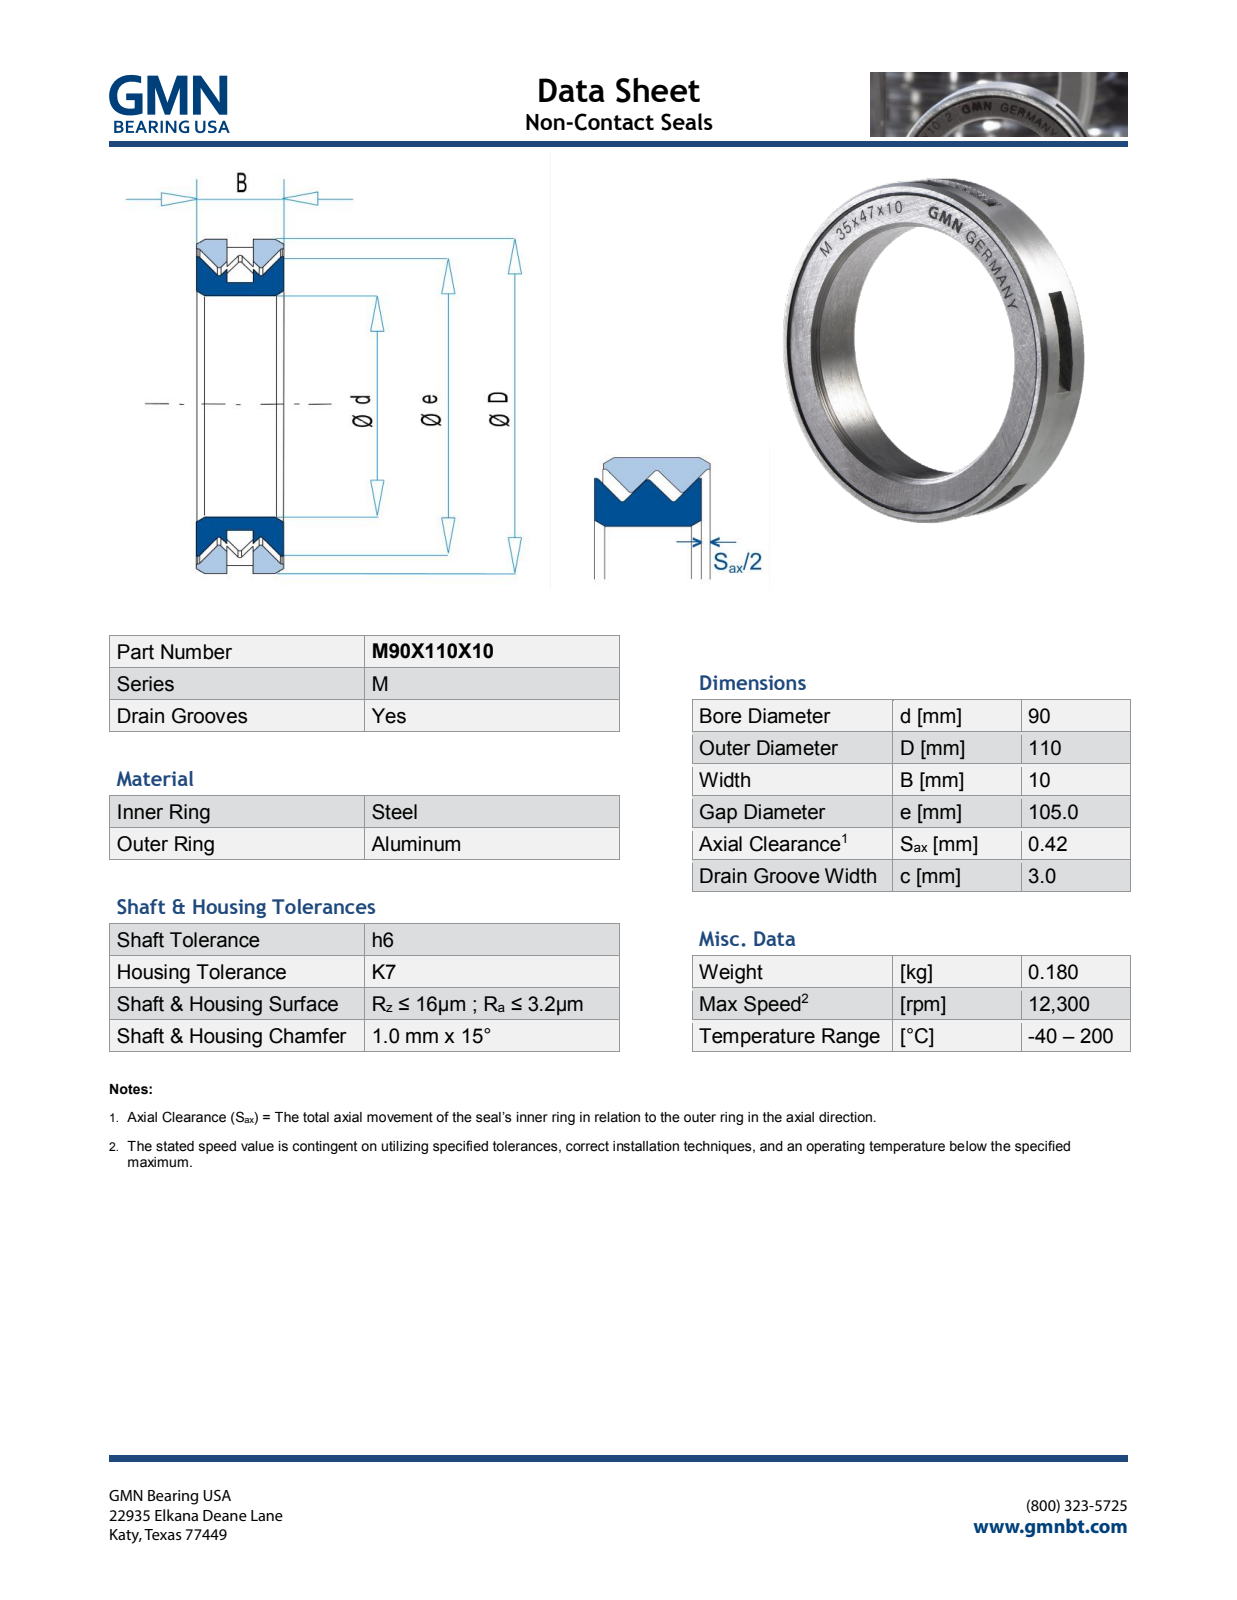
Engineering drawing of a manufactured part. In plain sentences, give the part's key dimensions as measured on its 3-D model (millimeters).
The part is named "M90X110X10_PRT". Its 3-D file was written by "PRO/ENGINEER BY PARAMETRIC TECHNOLOGY CORPORATION, 2013150 (AUTOMOTIVE_DESIGN)". It is 2 solids with 657 faces: 570 planar, 33 cylindrical and 54 other. Overall it measures 110 by 110 by 10.07 millimeters. Its volume is 29 083 cubic millimeters and its surface area 20 910 square millimeters. Round holes: 1 of diameter 90, 1 of diameter 105.3. Round bosses or shafts: 1 of diameter 110, 1 of diameter 105. Partial cylindrical surfaces (rounded edges, fillets, slot ends): 7 of radius 10. The main face-to-face distances are 10, 3.5, 6.5, 3, 3.57, 6.57, 10.07, 0.62, 4.31, 0.61.
